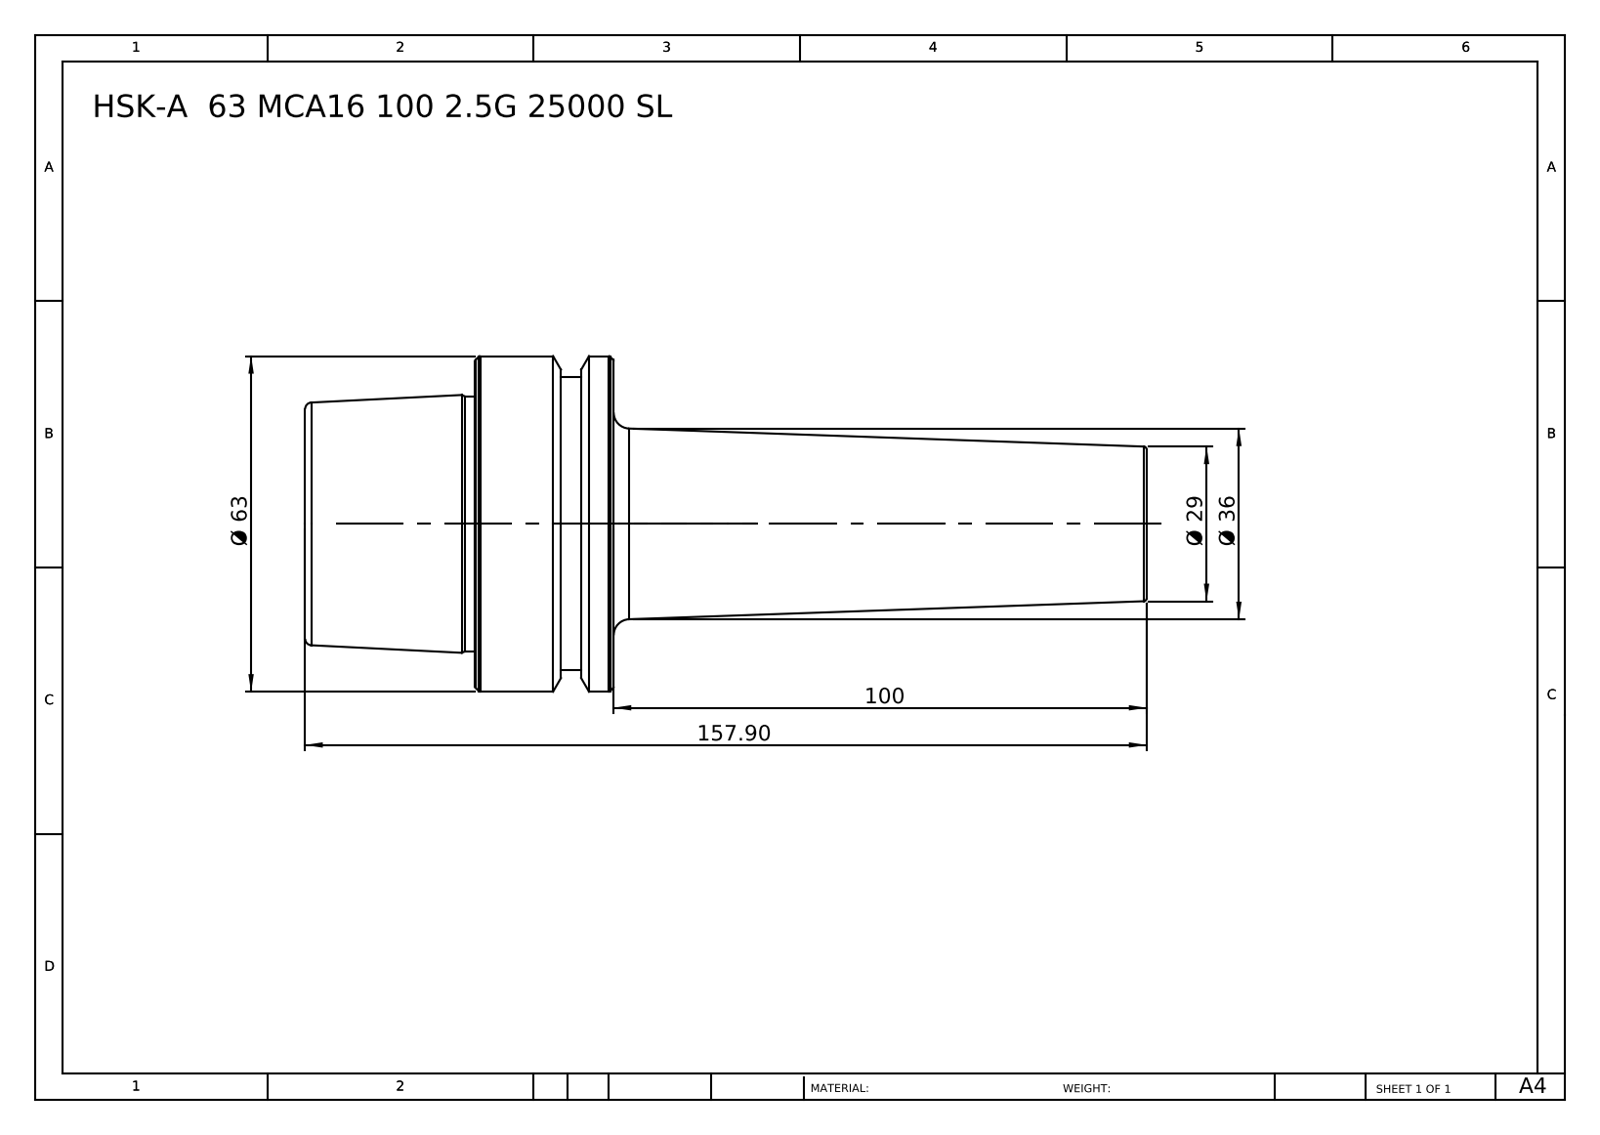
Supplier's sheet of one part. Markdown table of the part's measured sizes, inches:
| quantity | value |
| --- | --- |
| part name | HSK-A 63 MCA16 100 2.5G 25000 SL |
| STEP written by | SolidWorks 2014 (CONFIG_CONTROL_DESIGN) |
| units | inches |
| bodies | 1 solid, 46 faces (6 planar, 8 cylindrical, 32 other) |
| overall size | 6.217 × 2.48 × 2.48 |
| volume | 13.19 in³ |
| surface area | 40.86 in² |
| round bosses / shafts (diameter × count) | 2.48 × 1, 2.165 × 1, 1.881 × 1 |
| main face-to-face distances | 2.28, 1.024, 1.256, 3.937, 4.961, 6.217, 4.177, 0.24, 0.783, 2.039 |
